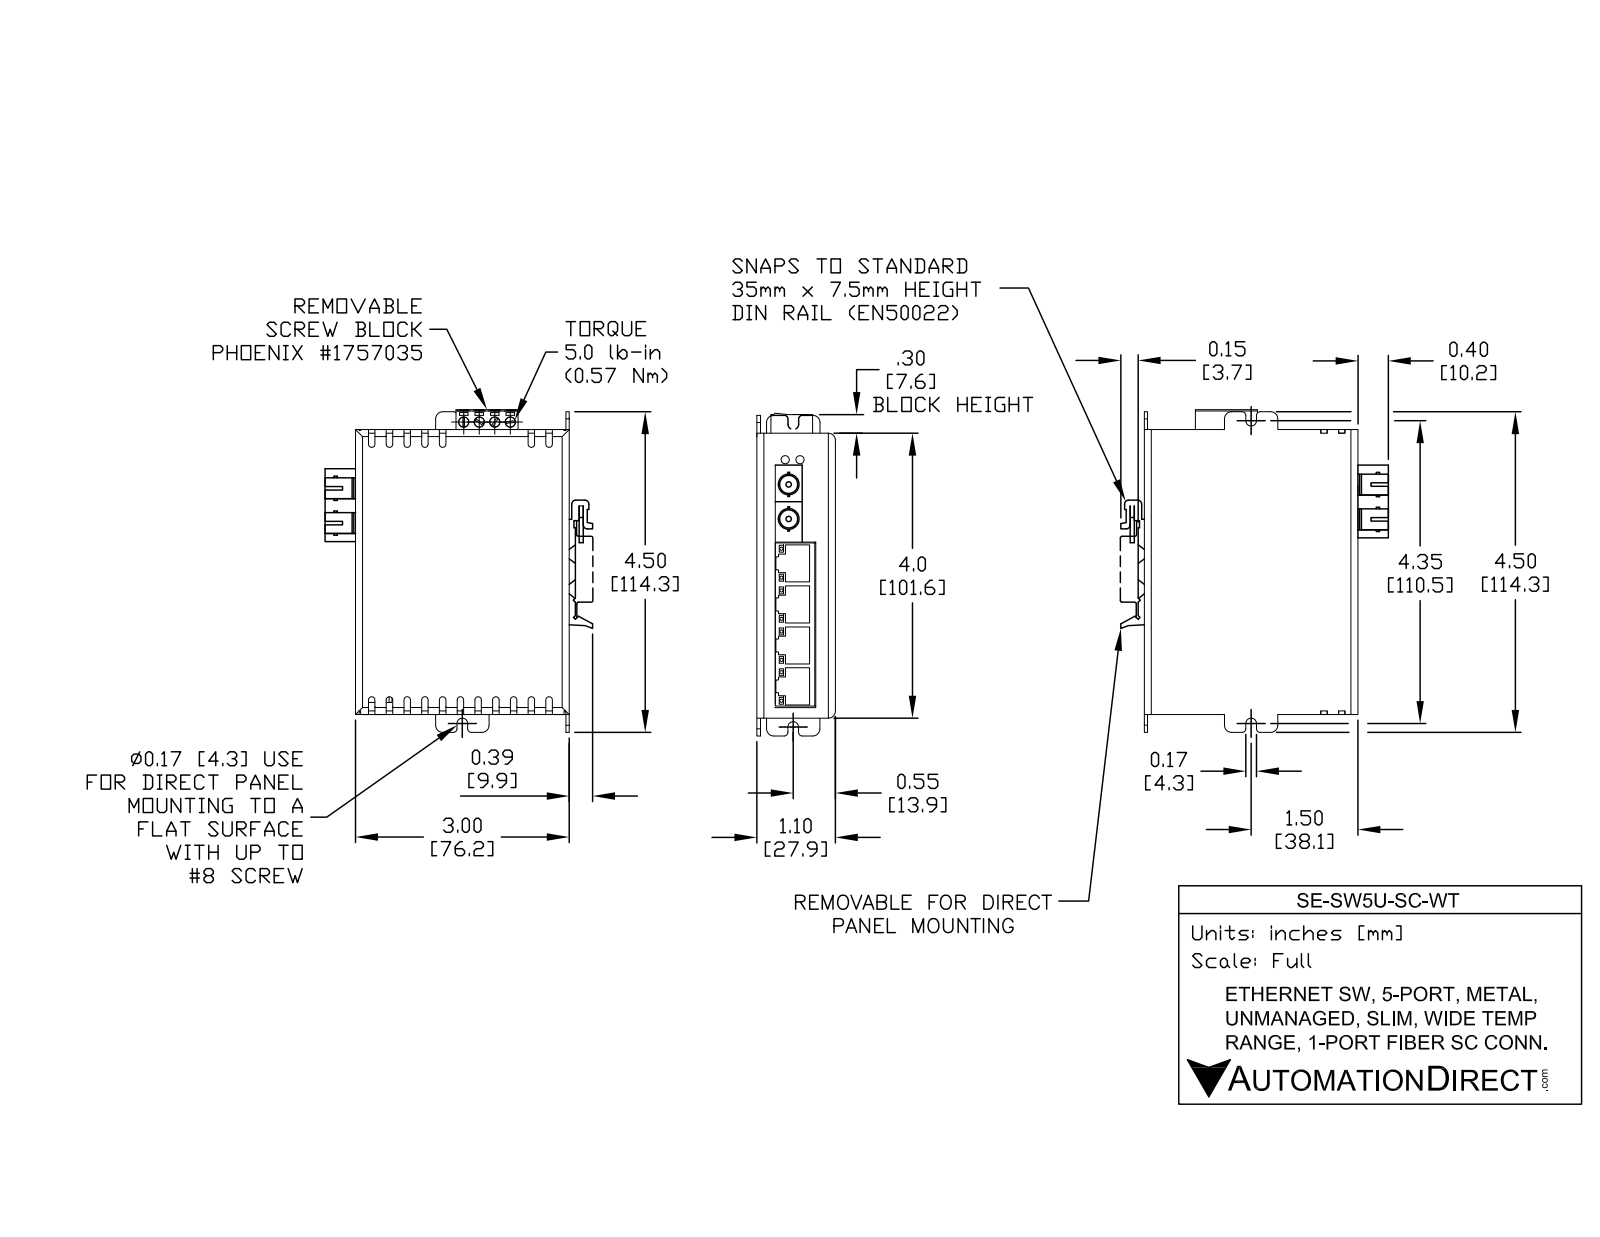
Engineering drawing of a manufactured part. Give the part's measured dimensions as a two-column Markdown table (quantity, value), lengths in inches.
| quantity | value |
| --- | --- |
| part name | SE-SW5U-SC-WT |
| STEP written by | SolidWorks 2011 (AUTOMOTIVE_DESIGN) |
| units | inches |
| bodies | 30 solids, 506 faces (386 planar, 49 cylindrical, 71 other) |
| overall size | 4.624 × 3.827 × 1.102 |
| volume | 1.759 in³ |
| surface area | 98.12 in² |
| round holes (diameter × count) | 0.15 × 4, 0.118 × 2 |
| round bosses / shafts (diameter × count) | 0.157 × 2, 0.334 × 1 |
| partial cylindrical surfaces (radius × count) | 0.05 × 8, 0.1 × 8, 0.039 × 5, 0.01 × 4, 0.057 × 3, 0.02 × 2, 0.049 × 2, 0.075 × 2 |
| main face-to-face distances | 0.02, 1.083, 1.102, 1.063, 3.98, 2.98, 0.551, 4, 3.961, 2.961 |
| hole center spacings | 0.2, 0.4, 0.511, 0.6 |
